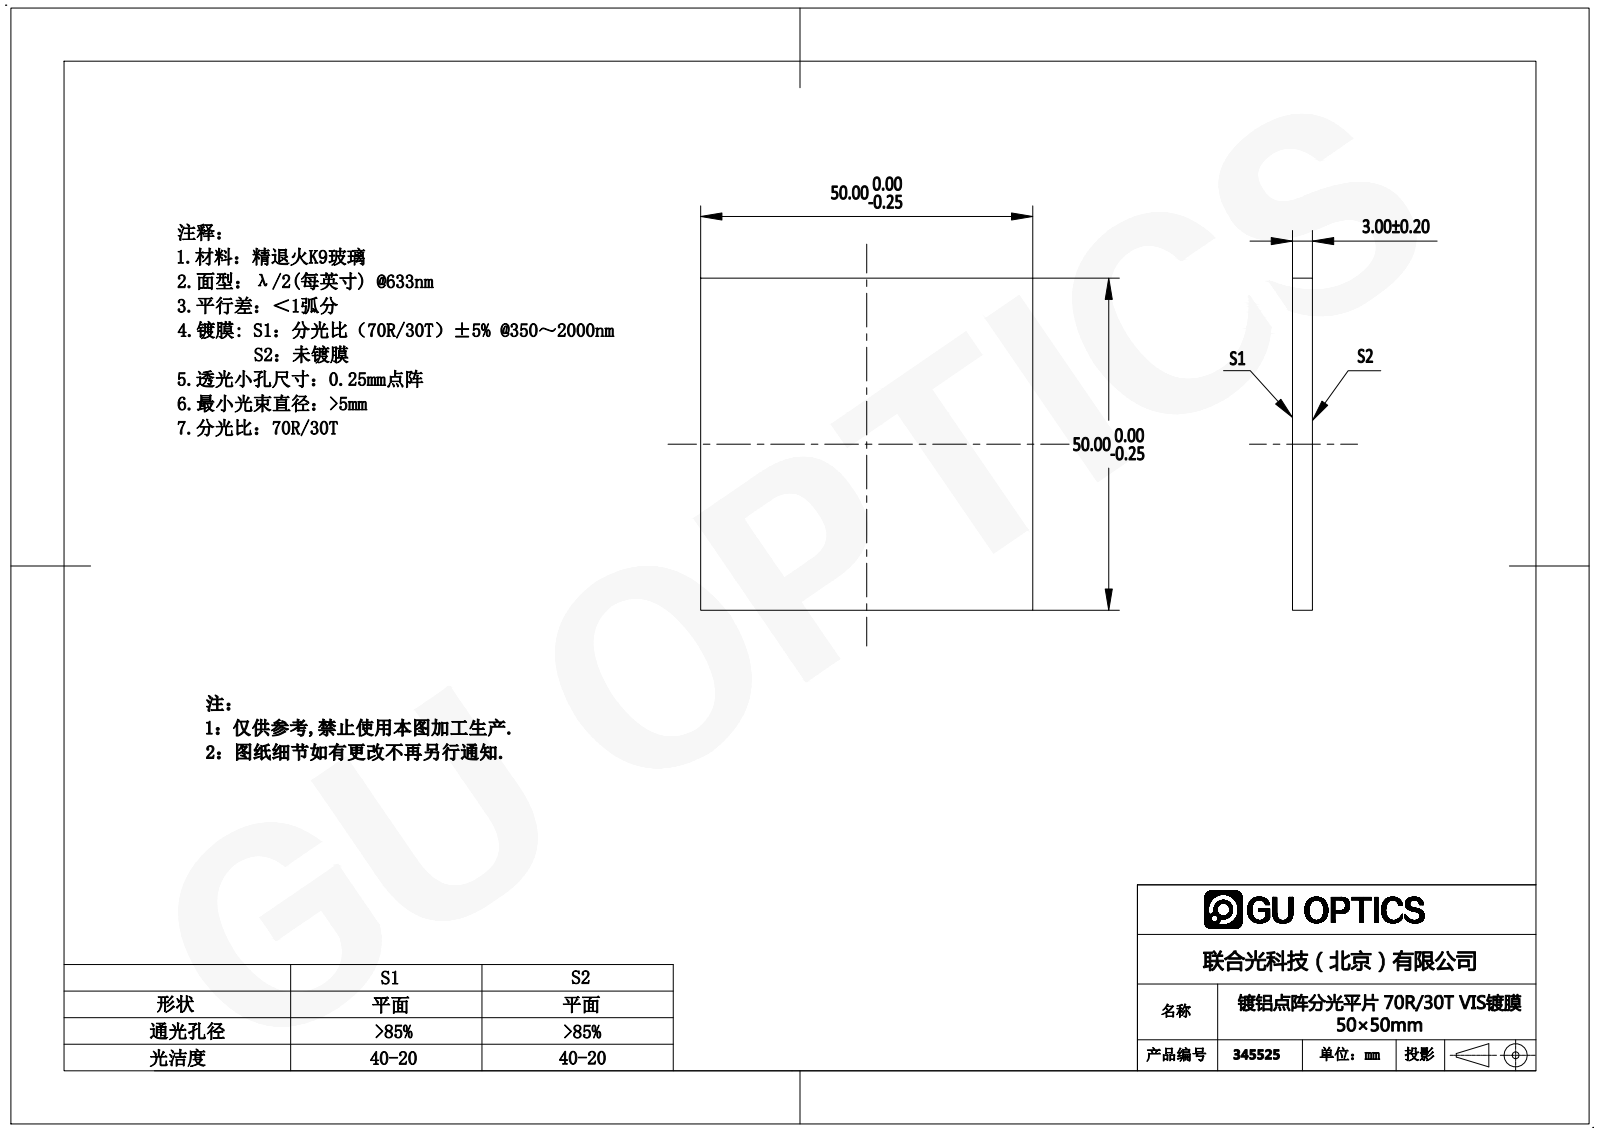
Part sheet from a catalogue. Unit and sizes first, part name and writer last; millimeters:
Units: millimetres
Overall size (bounding box): 50 × 50 × 3
Main face-to-face distances: 3, 50
Volume: 7 500 mm³ · Surface area: 5 600 mm²
Bodies: 1 solid, 6 faces (6 planar, 0 cylindrical, 0 other)
Part name (STEP PRODUCT): 345507
STEP written by: SolidWorks 2016 (AUTOMOTIVE_DESIGN)
